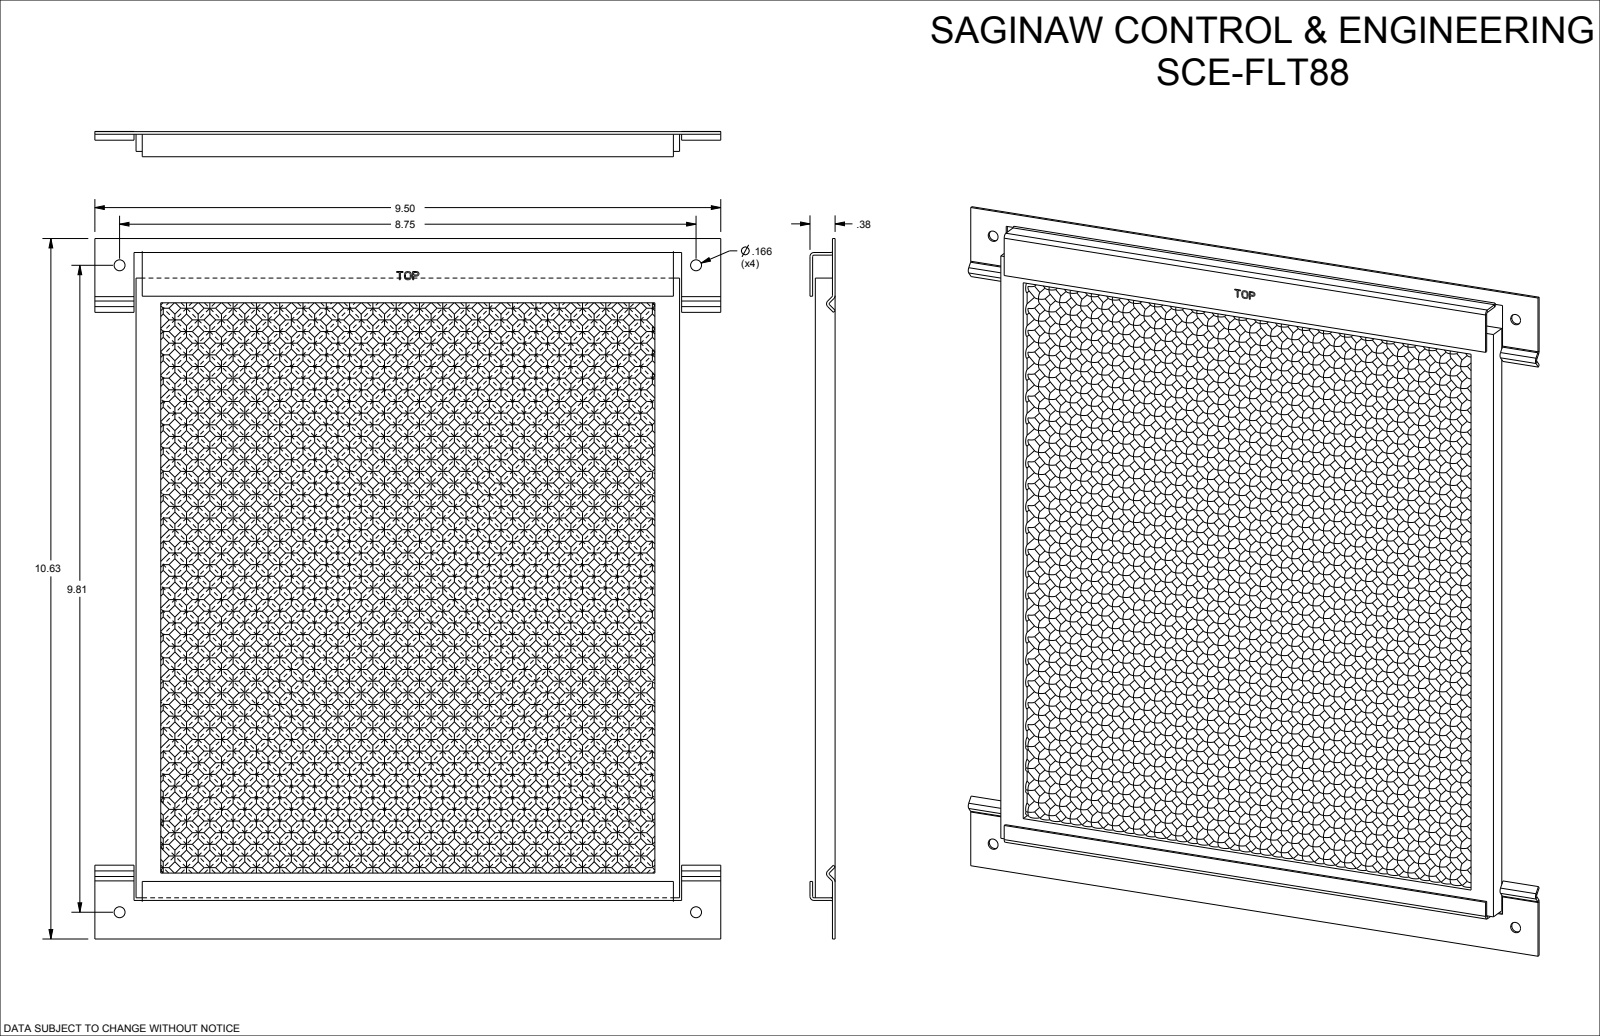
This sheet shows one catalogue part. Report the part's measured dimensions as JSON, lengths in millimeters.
{"part_name": "SCE-FLT88", "step_written_by": "SolidWorks 2019 (CONFIG_CONTROL_DESIGN)", "units": "millimeters", "bodies": {"solids": 3, "faces": 6460, "planar": 2200, "cylindrical": 4260, "other": 0}, "overall_size": [269.9, 241.3, 9.8], "volume_mm3": 164000, "surface_area_mm2": 161800, "round_holes": [[4.2, 4]], "round_bosses_or_shafts": [[3.2, 77], [3.2, 15]], "partial_cylinders_radius": [[0.5, 8], [1.5, 8]], "face_to_face_distances": [4.1, 0.5, 3.6, 1, 3.6, 4.1, 7.6, 2.5, 6.6, 3], "hole_center_spacings": [222.3, 249.3, 334]}
